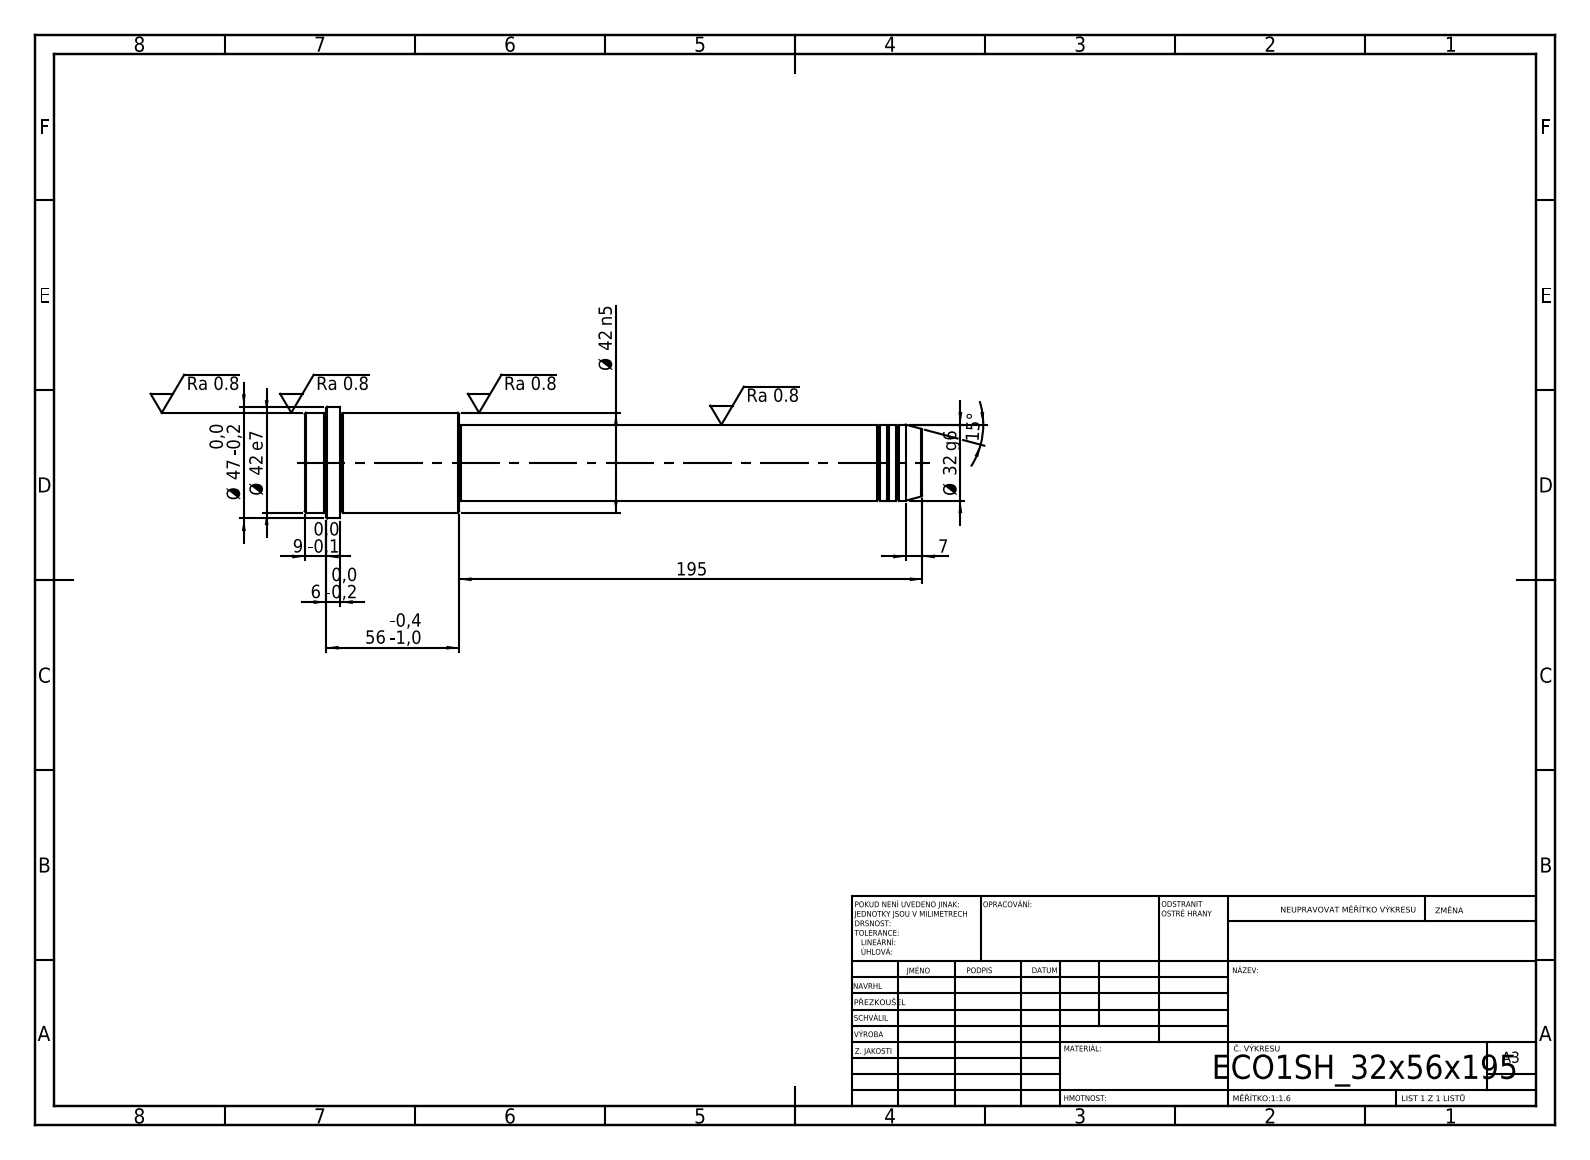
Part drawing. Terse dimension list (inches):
written by: SolidWorks 2019 (CONFIG_CONTROL_DESIGN)
unit: in
bodies: 1 solid, 52 faces (6 planar, 16 cylindrical, 30 other)
size: 10.236 × 1.85 × 1.85
volume: 15.14 in³; area: 49.32 in²
bosses: 1× ⌀1.85, 1× ⌀1.654, 1× ⌀1.26, 1× ⌀1.22
face distances: 10.236, 7.677, 2.559, 9.646, 1.969, 0.591, 9.882, 2.205, 0.236, 0.354
